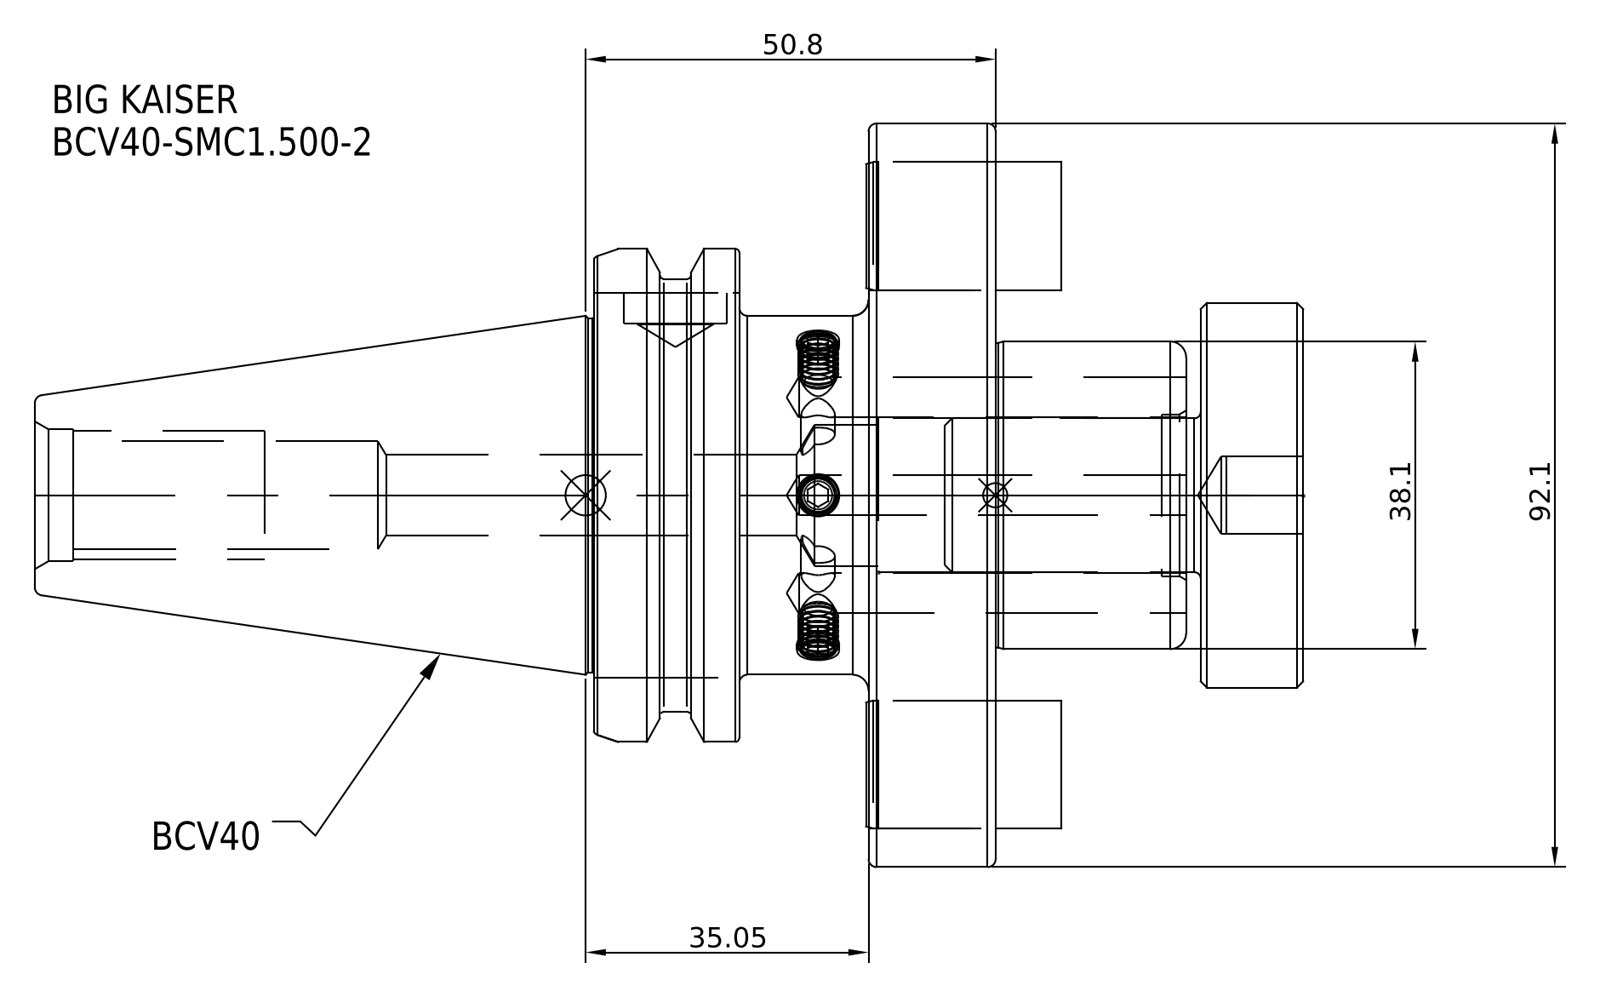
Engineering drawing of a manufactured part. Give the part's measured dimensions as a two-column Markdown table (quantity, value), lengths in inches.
| quantity | value |
| --- | --- |
| part name | BCV40-SMC1_500-2 |
| STEP written by | SolidWorks 2021 (CONFIG_CONTROL_DESIGN) |
| units | inches |
| bodies | 1 solid, 38 faces (18 planar, 14 cylindrical, 6 other) |
| overall size | 5.005 × 3.626 × 3.626 |
| volume | 15.31 in³ |
| surface area | 56.04 in² |
| round holes (diameter × count) | 0.687 × 1 |
| round bosses / shafts (diameter × count) | 3.626 × 1, 2.5 × 1, 2.219 × 1, 1.75 × 1 |
| main face-to-face distances | 0.62, 1.961, 1.341, 1.25, 0.63, 0.711, 0.625, 0.318, 0.938, 1.568 |
